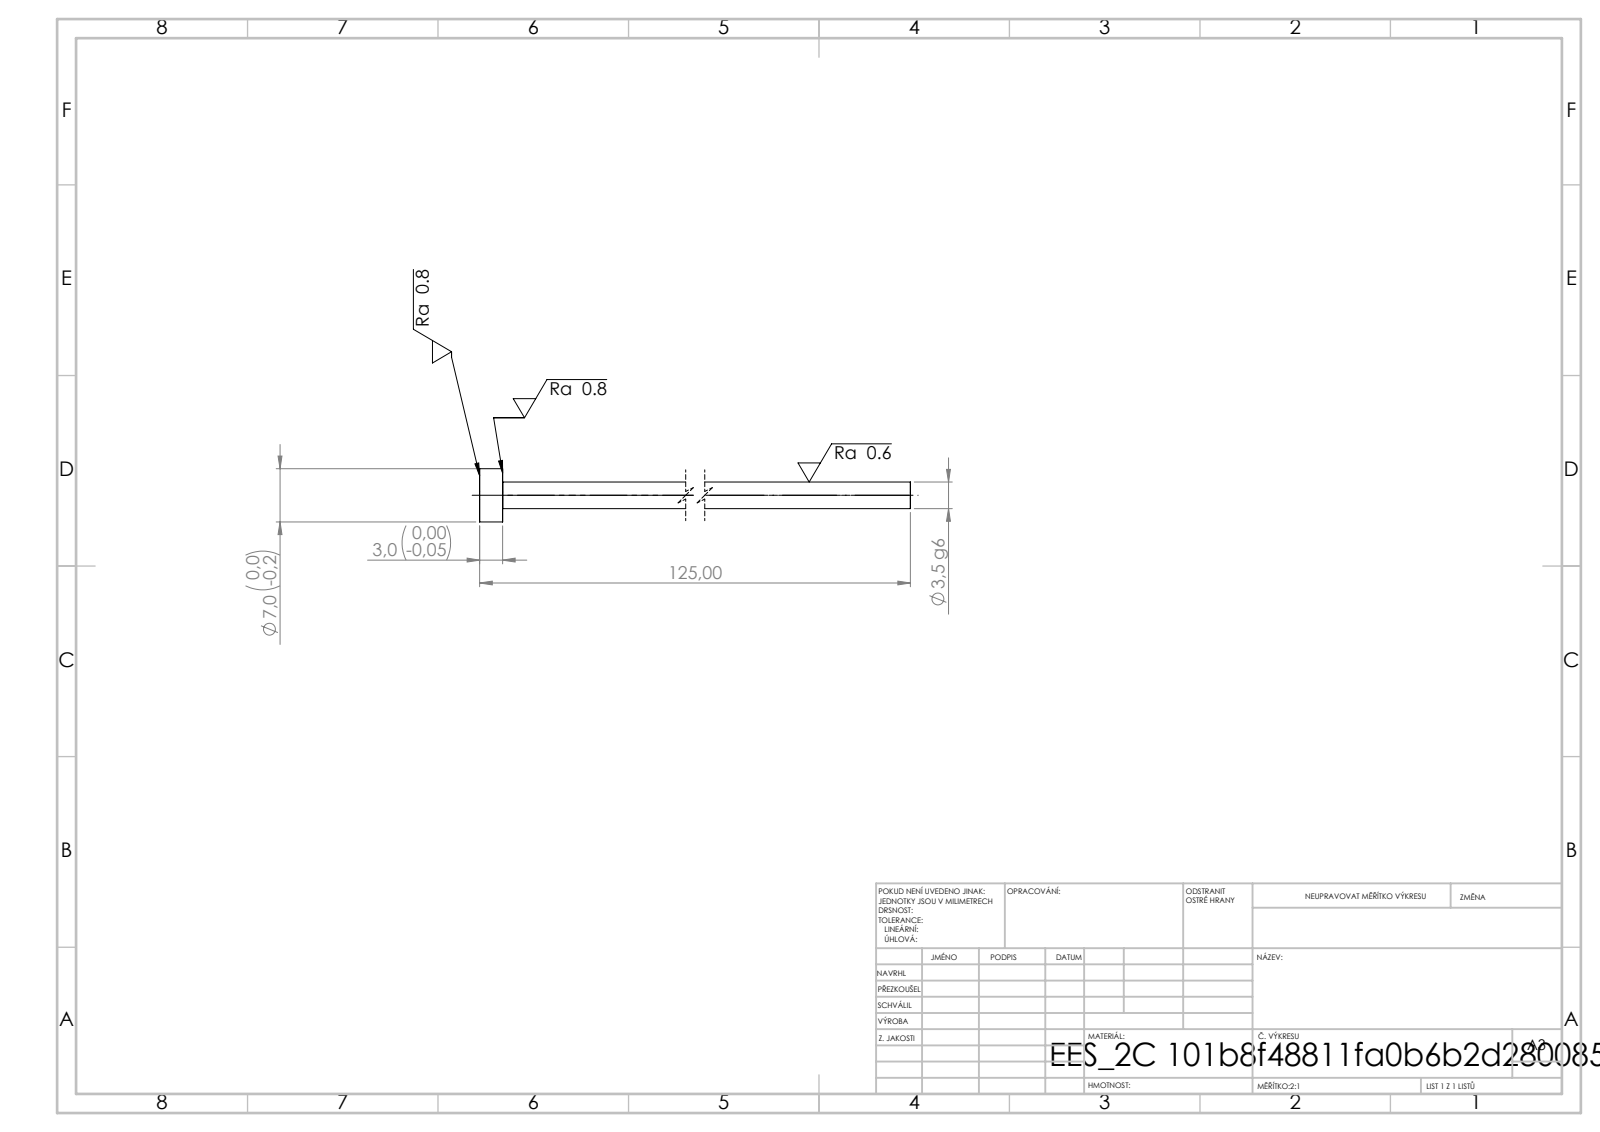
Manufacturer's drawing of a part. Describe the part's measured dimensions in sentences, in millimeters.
Its 3-D file was written by "SolidWorks 2019 (CONFIG_CONTROL_DESIGN)". It is 1 solid with 7 faces: 3 planar, 4 cylindrical and 0 other. Overall it measures 125 by 7 by 7 millimeters. Its volume is 1 289 cubic millimeters and its surface area 1 484 square millimeters. Round bosses or shafts: 1 of diameter 7, 1 of diameter 3.5. The main face-to-face distances are 3, 125, 122.
